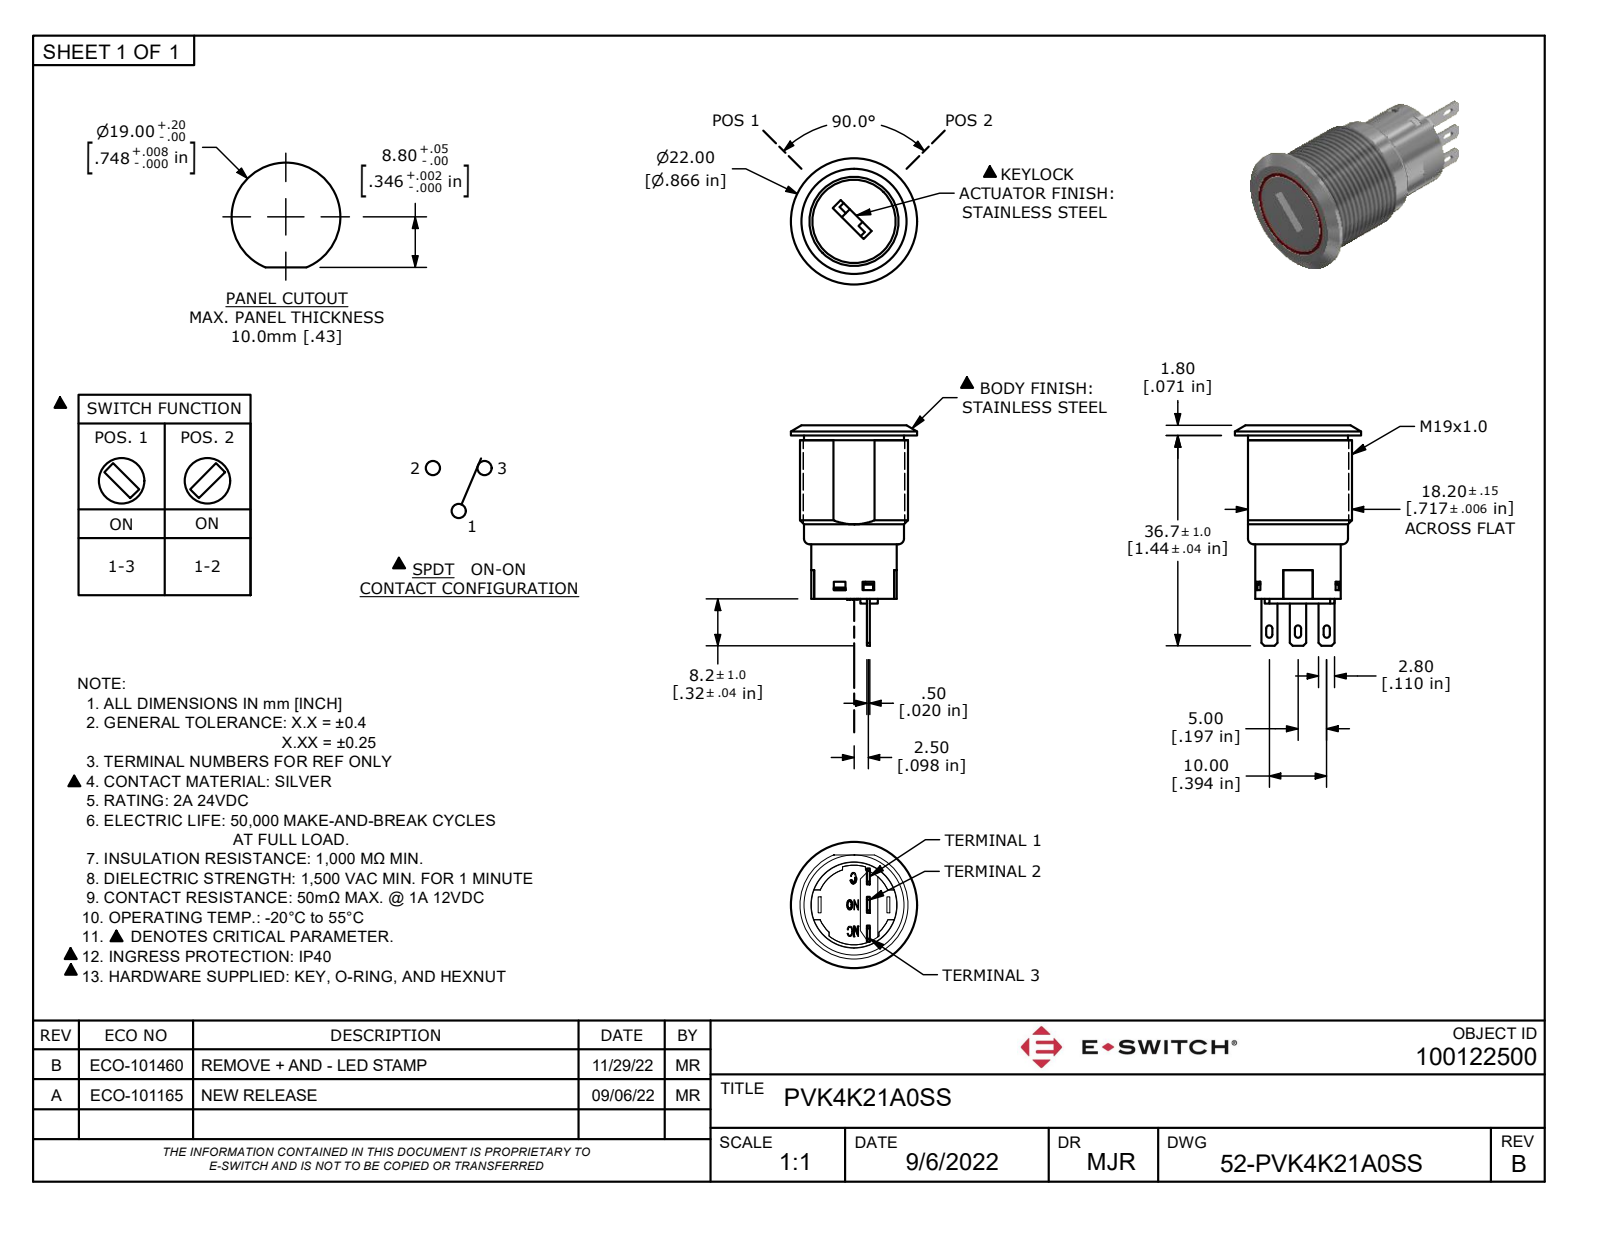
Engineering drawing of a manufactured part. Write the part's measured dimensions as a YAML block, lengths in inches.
part_name: "PVK4K21x0SS"
step_written_by: "Autodesk Inventor 2020 (AUTOMOTIVE_DESIGN)"
units: inches
bodies: {solids: 2, faces: 219, planar: 153, cylindrical: 30, other: 36}
overall_size: [1.516, 0.866, 0.866]
volume: 0.569
surface_area: 6.034
round_holes:
  - {diameter: 0.539, count: 1}
  - {diameter: 0.591, count: 1}
  - {diameter: 0.689, count: 1}
  - {diameter: 0.866, count: 1}
round_bosses_or_shafts:
  - {diameter: 0.744, count: 1}
  - {diameter: 0.622, count: 1}
  - {diameter: 0.61, count: 1}
  - {diameter: 0.587, count: 1}
  - {diameter: 0.571, count: 1}
partial_cylinders:
  - {radius: 0.022, count: 6}
  - {radius: 0.254, count: 1}
  - {radius: 0.274, count: 1}
face_to_face_distances: [0.016, 0.055, 0.071, 0.602, 0.52, 1.193, 0.657, 1.177, 0.118, 1.059]
